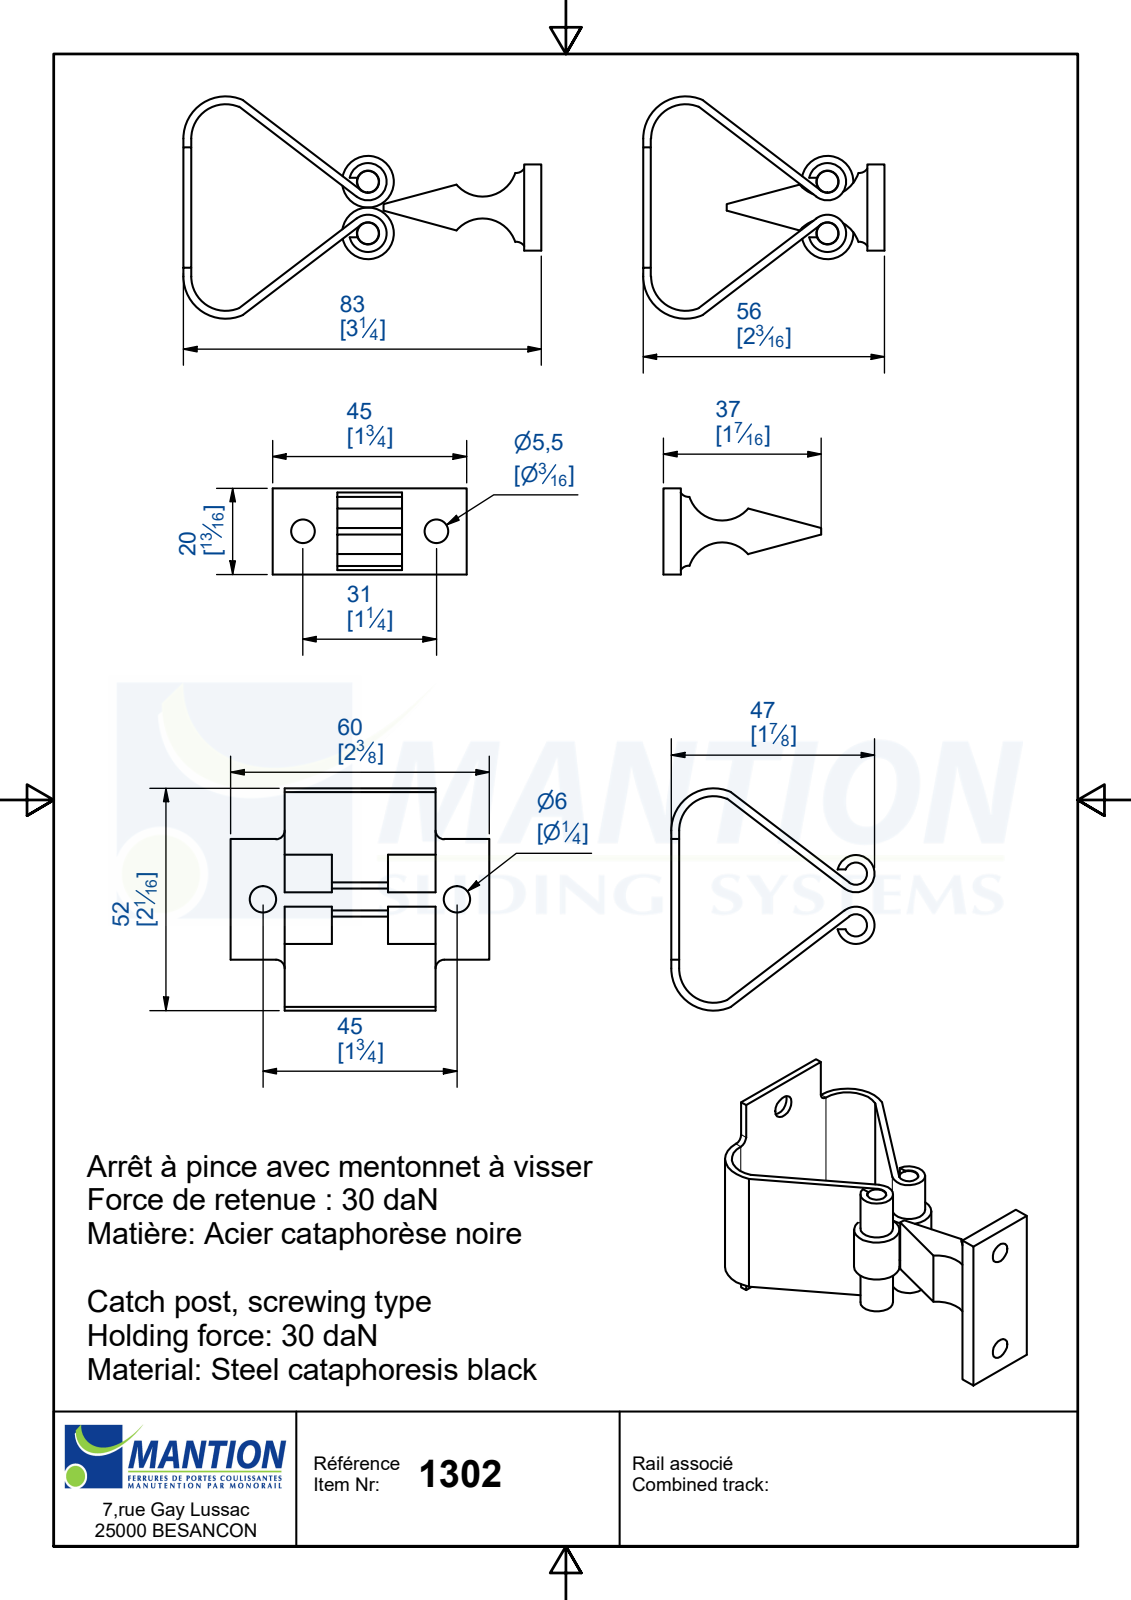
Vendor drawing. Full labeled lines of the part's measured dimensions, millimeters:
Part name (STEP PRODUCT): 1302; 15076; 15658; 15075 (+1 more)
STEP written by: Autodesk Inventor 2010 (AUTOMOTIVE_DESIGN)
Units: millimetres
Bodies: 6 solids, 77 faces (42 planar, 30 cylindrical, 5 other)
Overall size (bounding box): 82.49 × 60 × 51.6
Volume: 21 644 mm³ · Surface area: 19 887 mm²
Round holes (diameter × count): ⌀5.1 ×2, ⌀5.5 ×2, ⌀6.1 ×2
Round bosses / shafts (diameter × count): ⌀12 ×2, ⌀8.7 ×2, ⌀5 ×2
Partial cylindrical surfaces — rounded edges, fillets, slot ends (radius × count): R2 ×4, R8 ×4, R9.8 ×2, R2.17 ×1, R2.23 ×1
Main face-to-face distances: 1.8, 1.79, 1.81, 80.51, 82.31, 4, 76.51, 78.31, 10, 25
Hole centre spacings: 7, 38, 12, 31, 45
